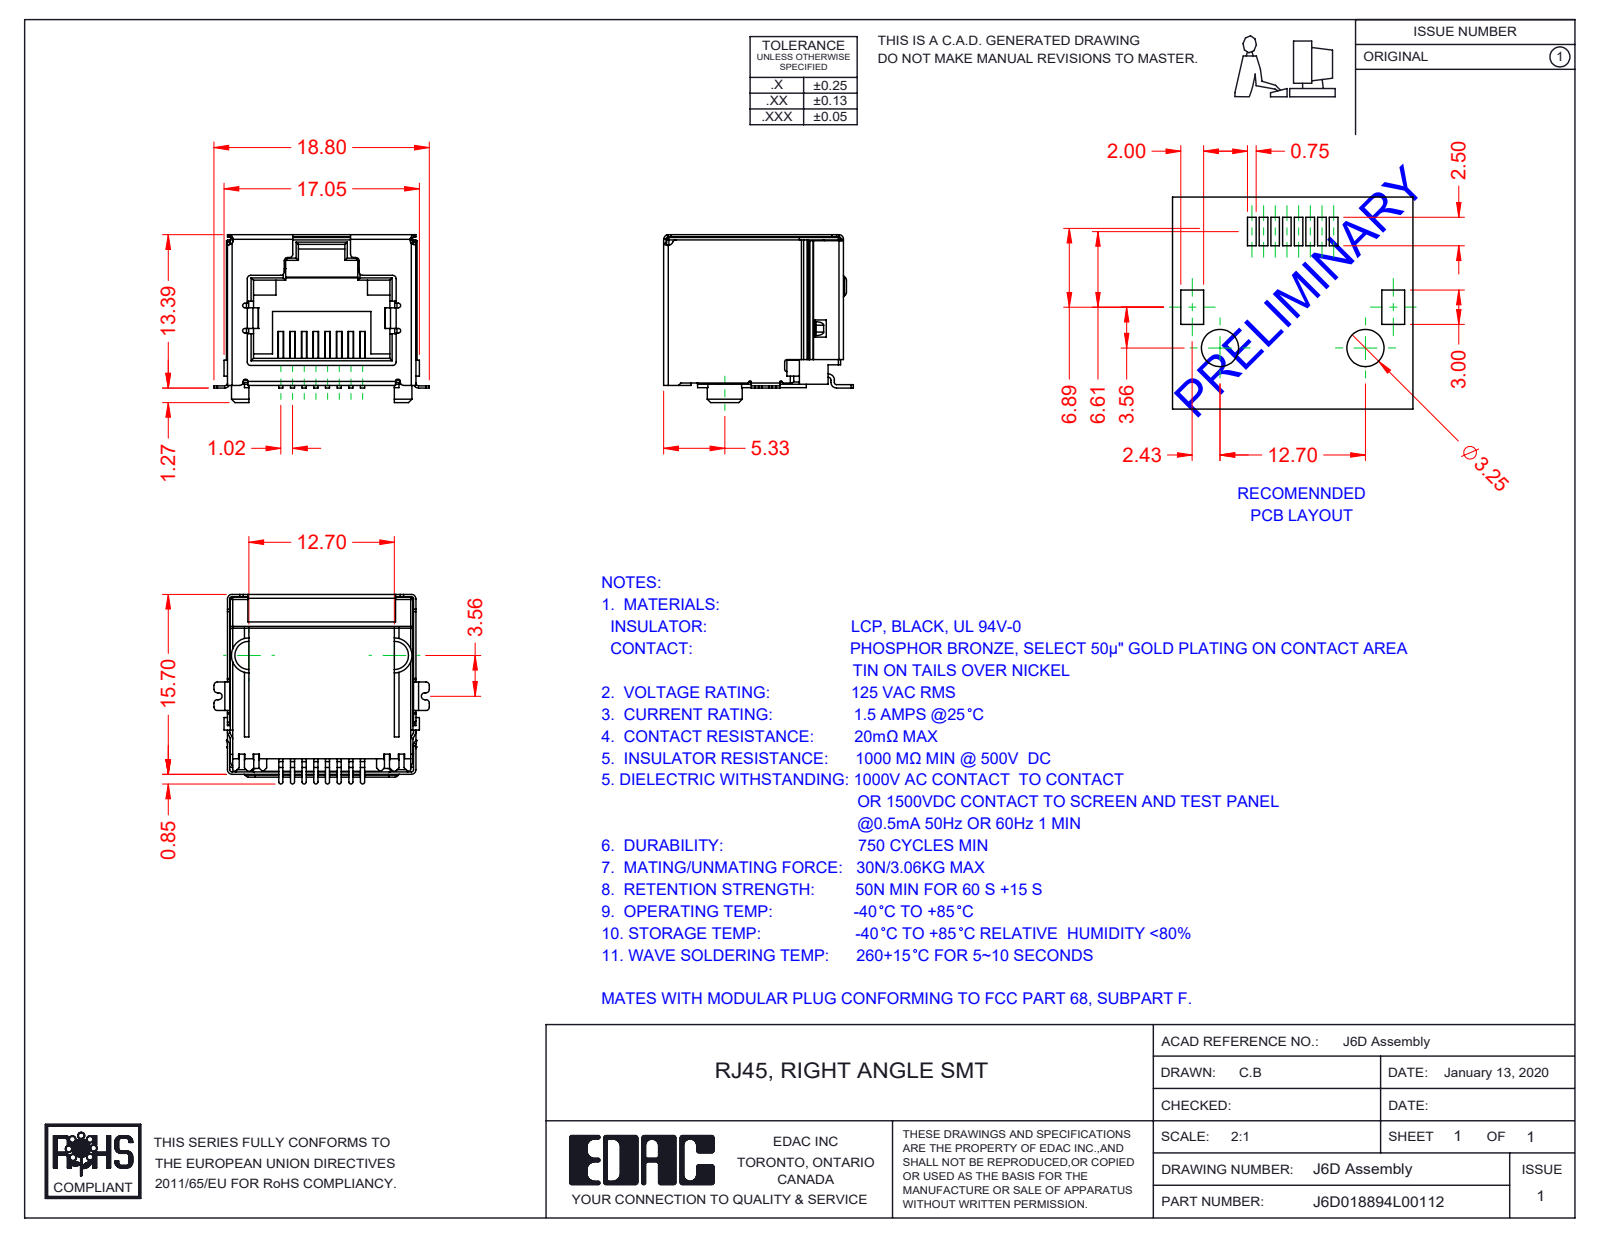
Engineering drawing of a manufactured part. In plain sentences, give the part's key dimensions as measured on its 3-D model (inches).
The part is named "6D Shield_No LED - No EMI; J6D018894L00112; 6D Contacts; 6D Insulator". Its 3-D file was written by "SolidWorks 2016 (CONFIG_CONTROL_DESIGN)". It is 10 solids with 827 faces: 596 planar, 198 cylindrical and 33 other. Overall it measures 0.74 by 0.652 by 0.577 inches. Its volume is 0.103 cubic inches and its surface area 7.113 square inches. Partial cylindrical surfaces (rounded edges, fillets, slot ends): 39 of radius 0.012, 37 of radius 0.008, 16 of radius 0.016, 12 of radius 0.004, 8 of radius 0.006, 8 of radius 0.007, 6 of radius 0.02, 3 of radius 0.014. The main face-to-face distances are 0.63, 0.64, 0.638, 0.089, 0.628, 0.018, 0.648, 0.514, 0.504, 0.417.
